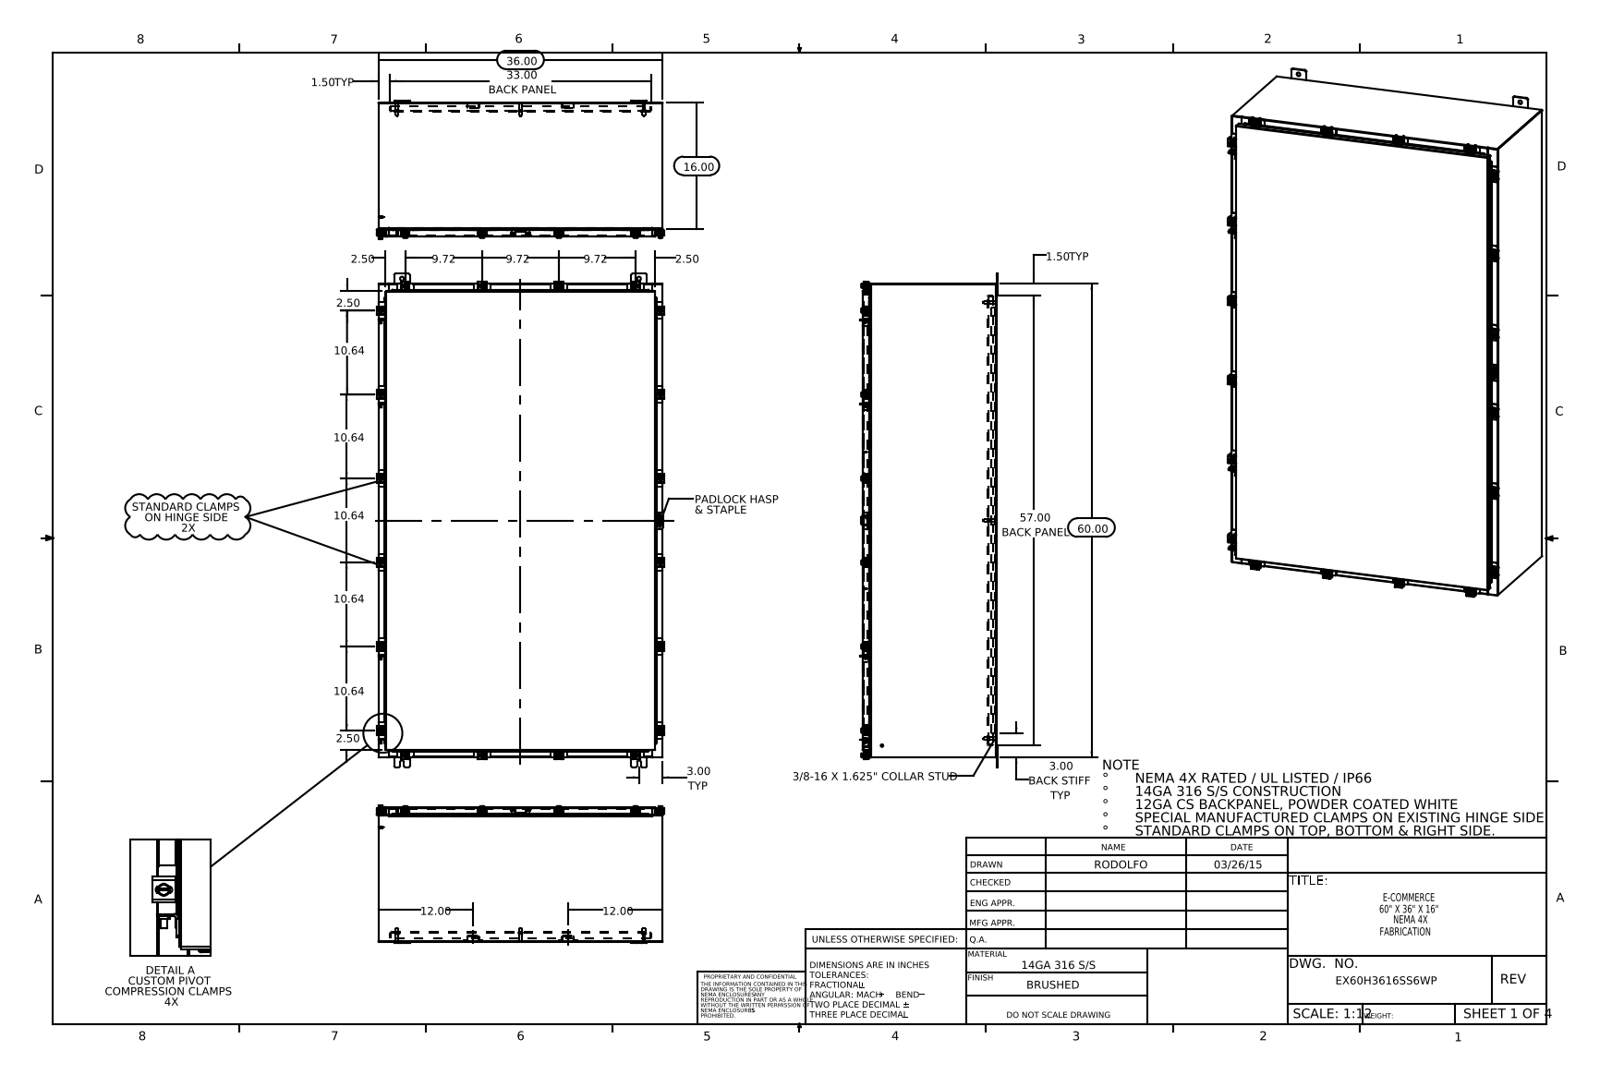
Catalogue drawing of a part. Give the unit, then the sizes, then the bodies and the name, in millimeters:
Units: millimetres
Overall size (bounding box): 1587.5 × 925.1 × 443.3
Round holes (diameter × count): ⌀5.4 ×20, ⌀6.6 ×20, ⌀12.7 ×12, ⌀6.4 ×9, ⌀3.2 ×1
Round bosses / shafts (diameter × count): ⌀12.7 ×20, ⌀6.4 ×20, ⌀10.1 ×16, ⌀15.9 ×8, ⌀9.5 ×8, ⌀8.4 ×8, ⌀4 ×8, ⌀3.6 ×8
Partial cylindrical surfaces — rounded edges, fillets, slot ends (radius × count): R1.5 ×84, R3.6 ×40, R0.3 ×38, R3 ×36, R2.2 ×34, R2.3 ×32, R1.3 ×29, R3.7 ×28
Main face-to-face distances: 1.9, 429.3, 427.4, 2.6, 431.2, 912.5, 25.4, 27.3, 402, 403.9
Hole centre spacings: 50, 56.5, 59.6, 354.9, 374.1, 409.6, 701.7, 755.5
Volume: 13 930 000 mm³ · Surface area: 13 690 000 mm²
Bodies: 140 solids, 3424 faces (1773 planar, 1319 cylindrical, 332 other)
Part name (STEP PRODUCT): EX60H3616SS6WP Standard Clamps; EX60H3616SS6WP Door Stiffener; Clamp Top_RTP31; EX60H3616SS6WP Special Clamp (+8 more)
STEP written by: SolidWorks 2014 (CONFIG_CONTROL_DESIGN)
